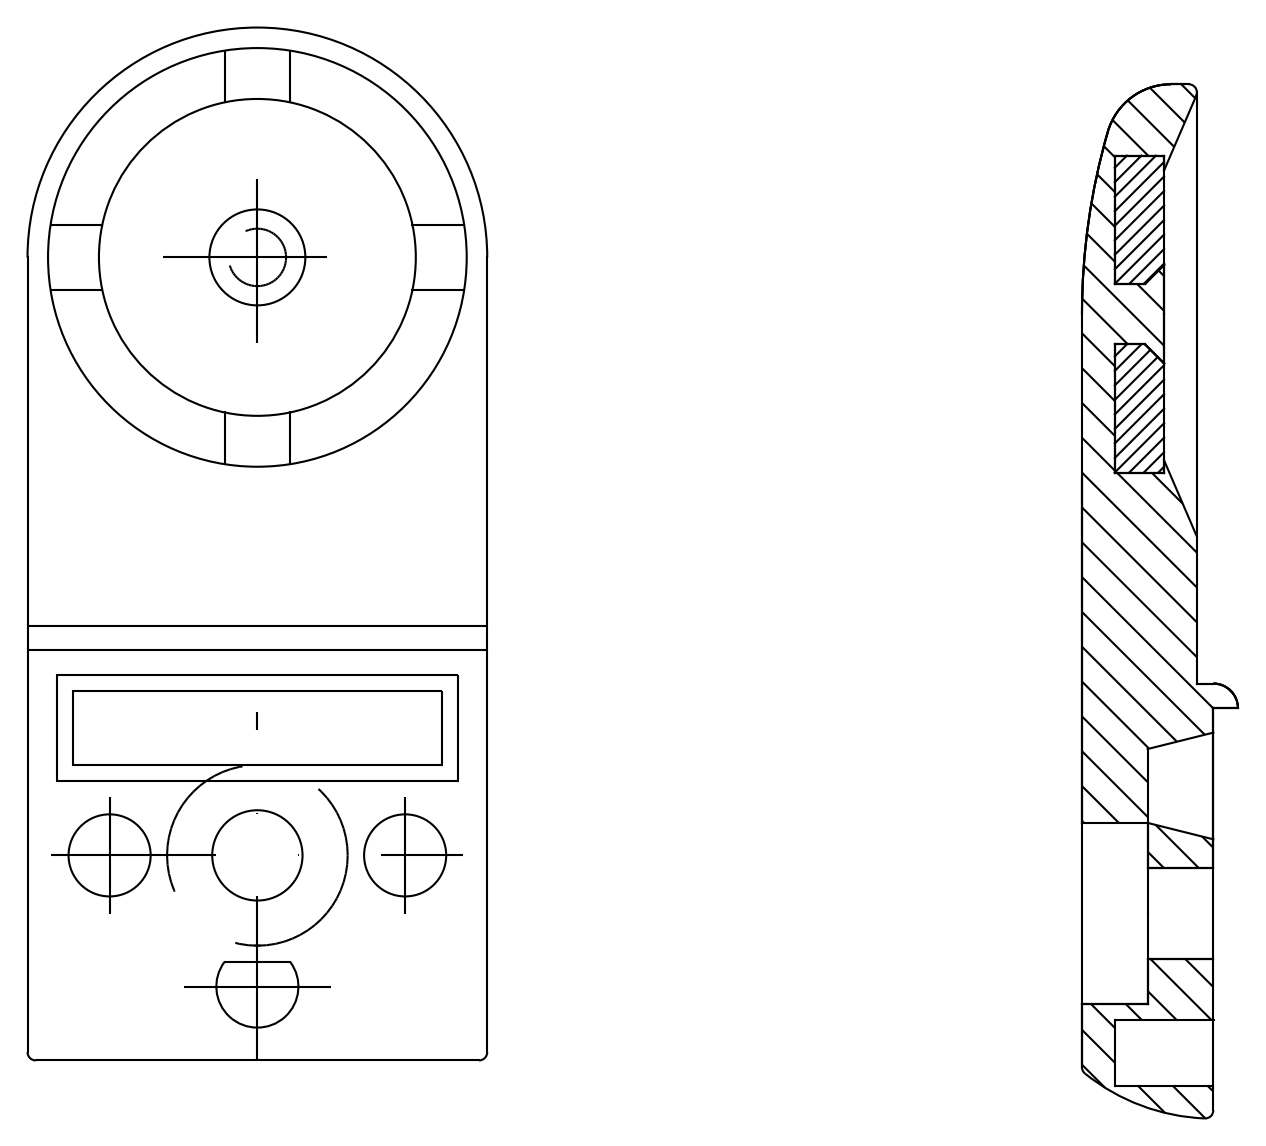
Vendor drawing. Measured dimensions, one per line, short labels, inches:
written by: THINKDESIGN (CONFIG_CONTROL_DESIGN)
unit: in
bodies: 2 solids, 67 faces (34 planar, 23 cylindrical, 10 other)
size: 2.476 × 1.102 × 0.373
volume: 0.562 in³; area: 8.809 in²
holes: 2× ⌀0.197, 1× ⌀0.217, 1× ⌀0.23, 1× ⌀0.428, 1× ⌀0.76
bosses: 1× ⌀0.766
rounds: 2× R0.157, 1× R0.058, 1× R0.098, 1× R0.489, 1× R0.49, 1× R0.502, 1× R0.551, 1× R1.575
face distances: 0.118, 0.236, 1.102, 0.079, 0.157, 0.039, 0.058, 0.63, 0.472, 0.863
hole spacings: 0.354, 1.477, 1.48, 0.709, 1.434, 1.437
